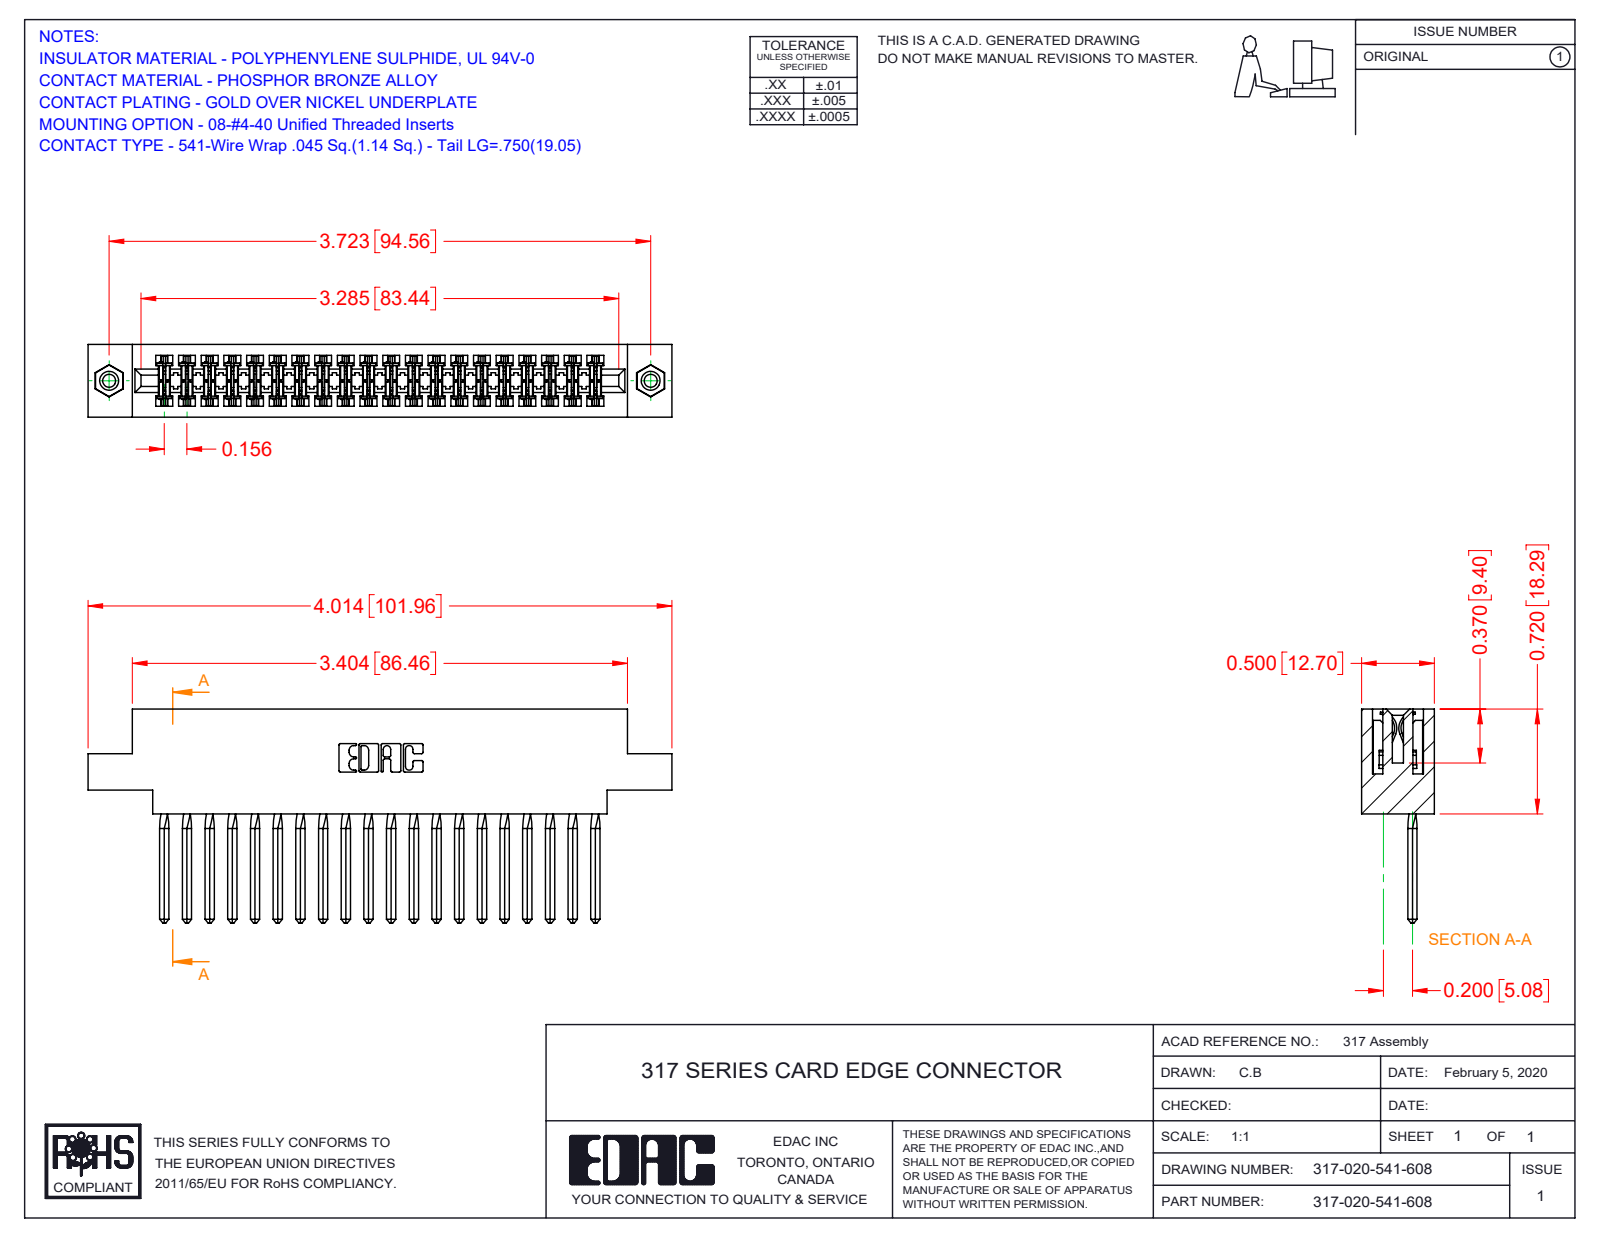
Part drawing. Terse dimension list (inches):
name: 317-290-002_541; 317 Part_.156 Dia - TI; 345-250-001_345-250-003-102; 317-020-541-678
written by: SolidWorks 2016 (CONFIG_CONTROL_DESIGN)
unit: in
bodies: 23 solids, 3202 faces (2570 planar, 536 cylindrical, 96 other)
size: 4.014 × 1.47 × 0.5
volume: 0.967 in³; area: 33.61 in²
holes: 2× ⌀0.089, 2× ⌀0.125, 2× ⌀0.156
bosses: 2× ⌀0.155
rounds: 40× R0.015, 22× R0.01, 6× R0.007, 6× R0.031, 3× R0.026, 2× R0.095, 2× R0.1, 2× R0.11
face distances: 0.5, 0.075, 0.425, 0.11, 0.35, 0.195, 0.772, 0.22, 0.662, 0.72
hole spacings: 3.723
